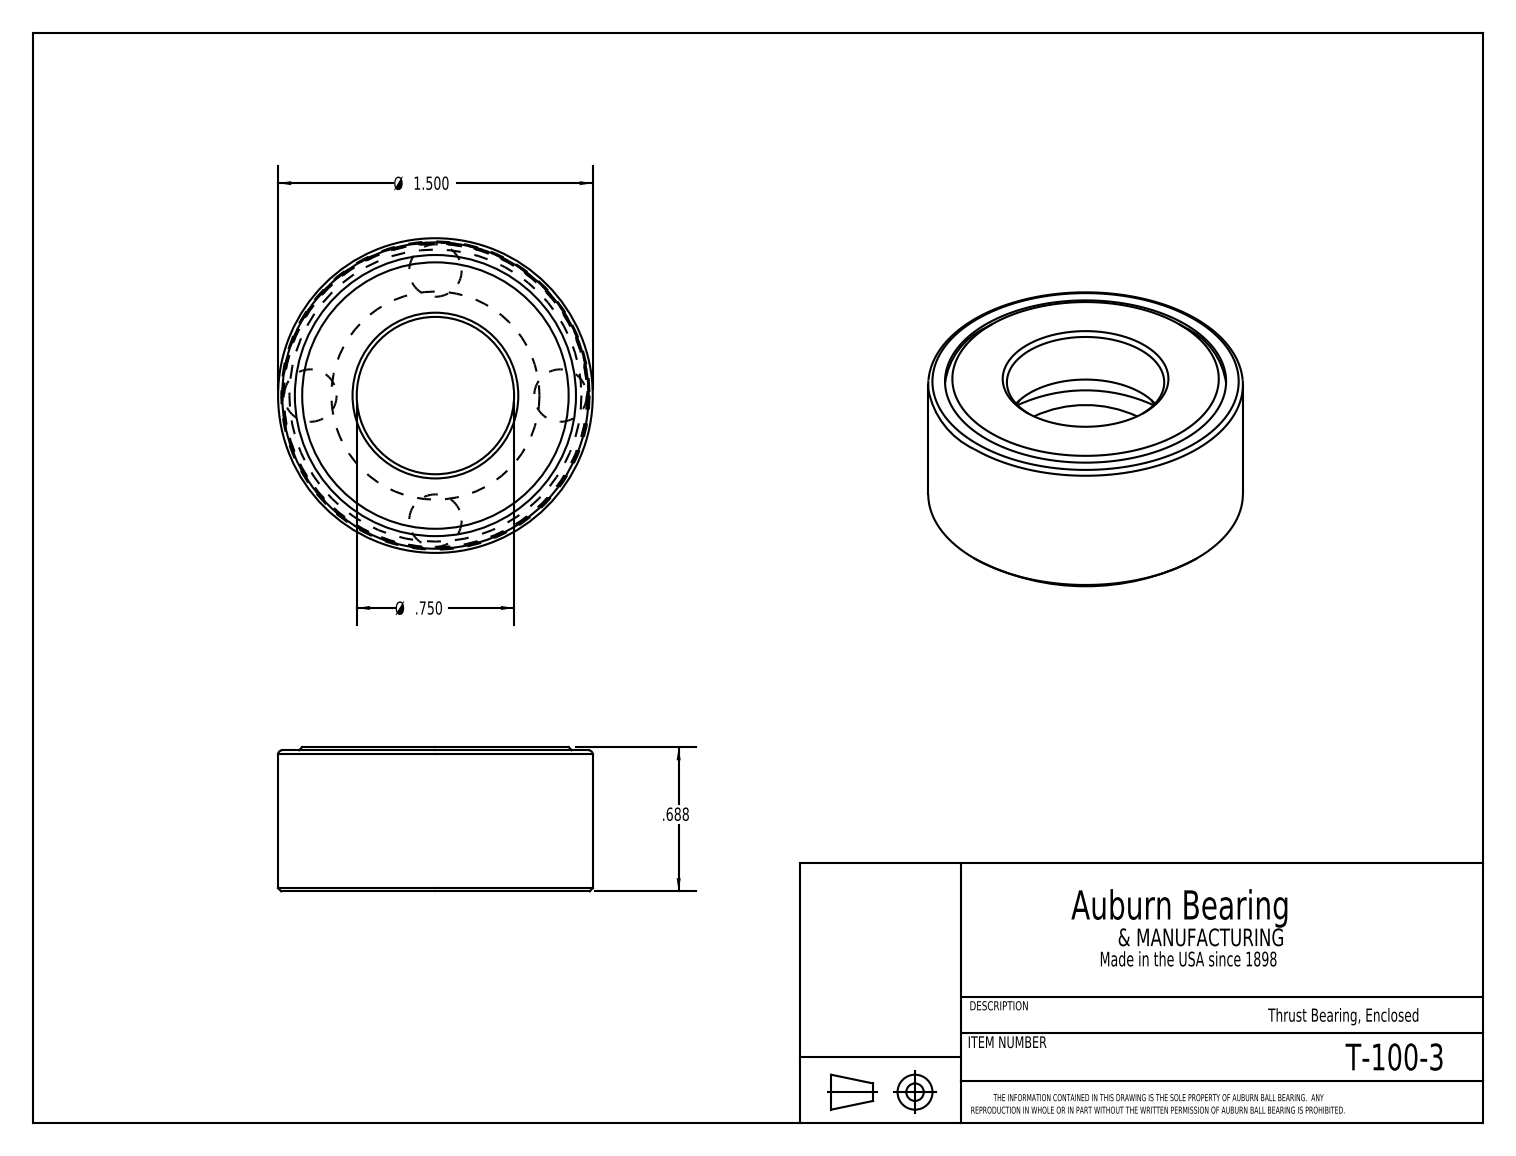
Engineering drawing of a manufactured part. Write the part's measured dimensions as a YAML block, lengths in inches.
part_name: "T-100-3"
step_written_by: "SolidWorks 2016 (CONFIG_CONTROL_DESIGN)"
units: inches
bodies: {solids: 6, faces: 28, planar: 9, cylindrical: 7, other: 12}
overall_size: [1.5, 1.5, 0.688]
volume: 0.683
surface_area: 13.76
round_holes:
  - {diameter: 0.75, count: 1}
  - {diameter: 1.34, count: 1}
  - {diameter: 1.46, count: 1}
round_bosses_or_shafts:
  - {diameter: 1.5, count: 1}
  - {diameter: 1.446, count: 1}
face_to_face_distances: [0.687, 0.269, 0.419, 0.419, 0.15, 0.269, 0.672, 0.404, 0.254, 0.015]
